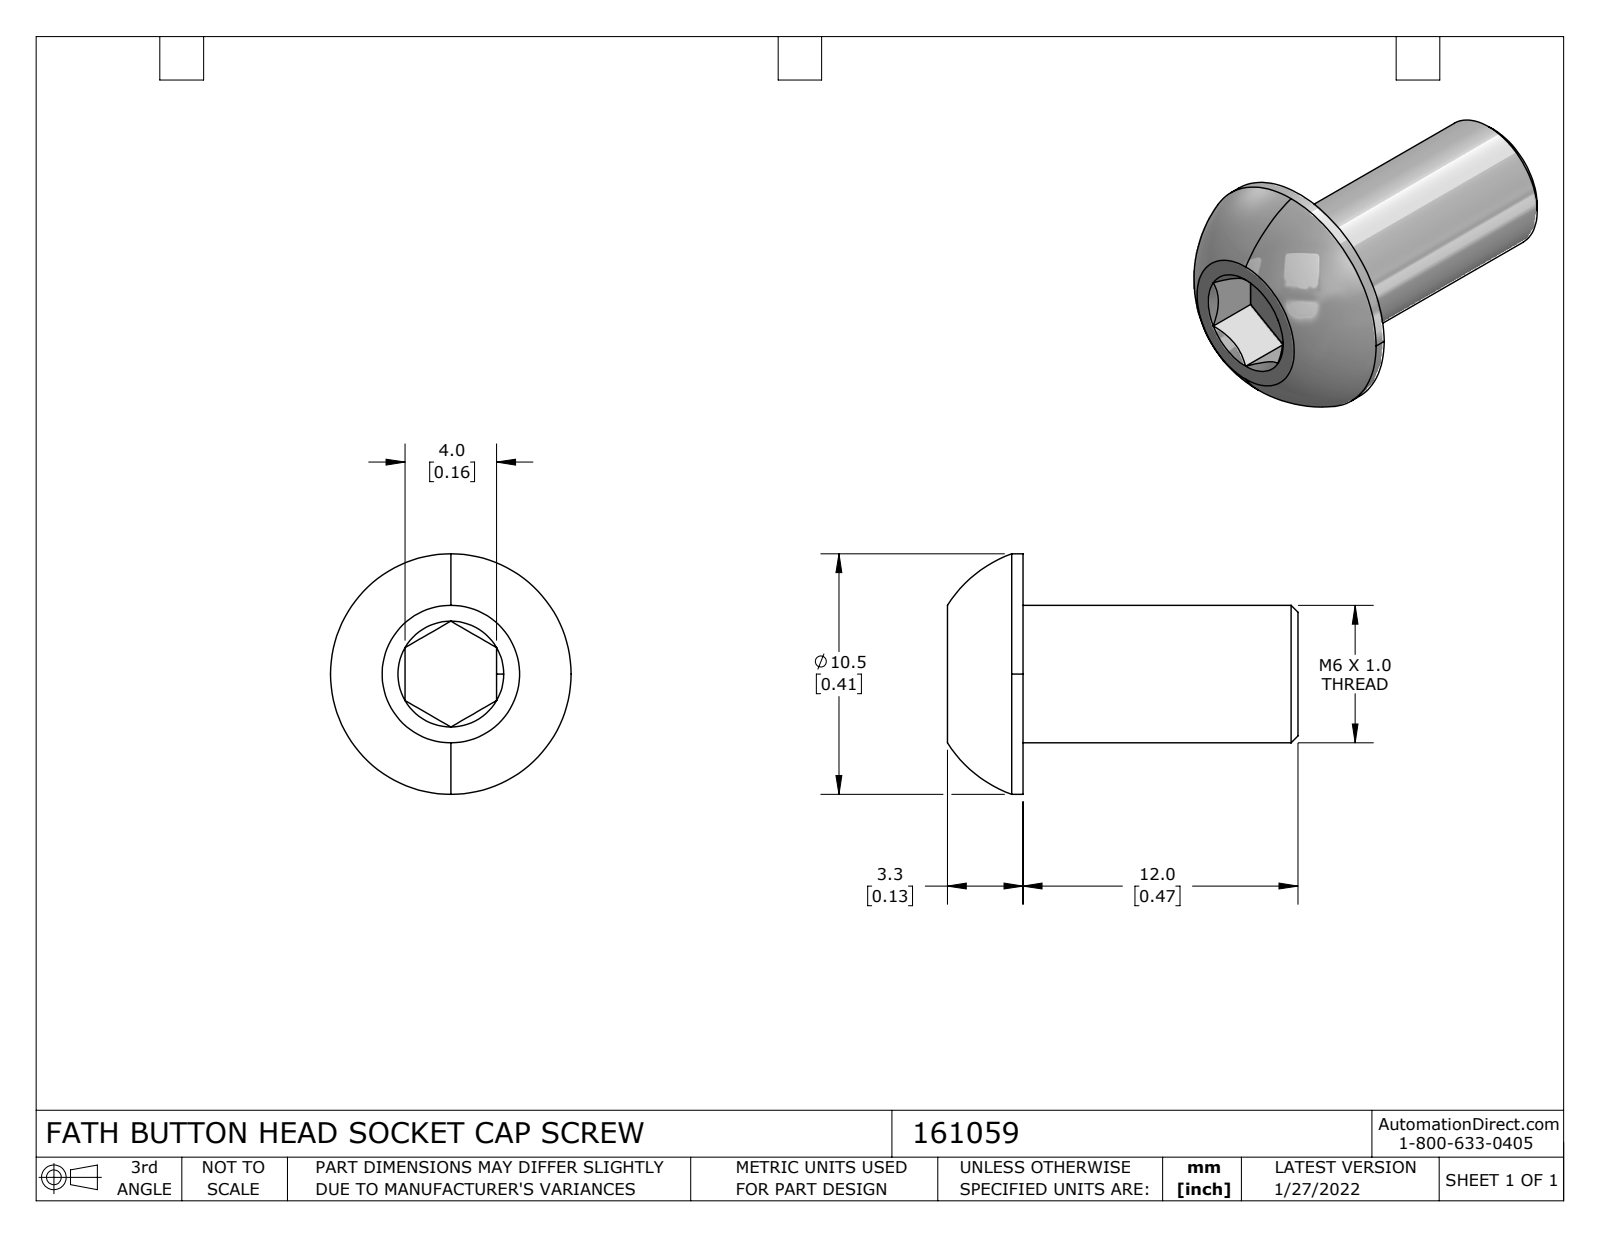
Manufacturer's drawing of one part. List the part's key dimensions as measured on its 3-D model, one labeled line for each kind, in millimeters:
Part name (STEP PRODUCT): 161059
STEP written by: SolidWorks 2021 (CONFIG_CONTROL_DESIGN)
Units: millimetres
Bodies: 1 solid, 25 faces (10 planar, 4 cylindrical, 11 other)
Overall size (bounding box): 15.3 × 10.5 × 10.5
Volume: 522 mm³ · Surface area: 483 mm²
Round bosses / shafts (diameter × count): ⌀10.5 ×1, ⌀6 ×1
Main face-to-face distances: 12, 4, 12.99, 0.99, 15.3, 3.3, 2.31
